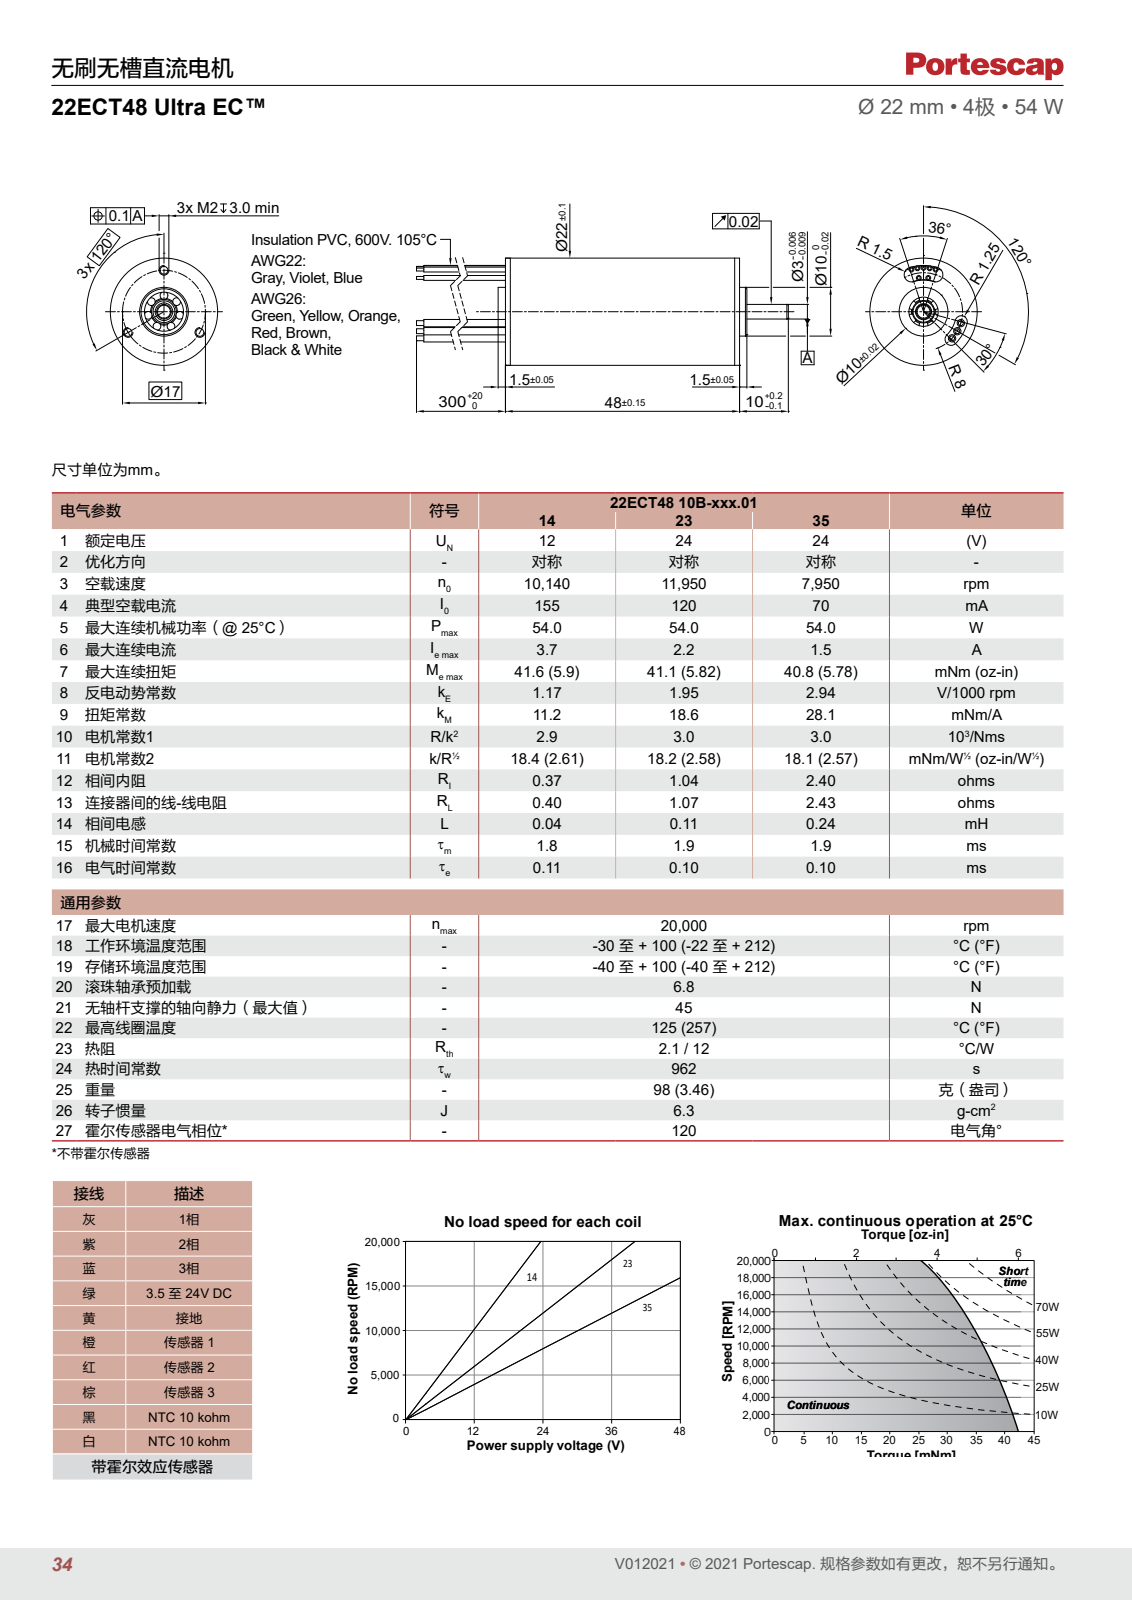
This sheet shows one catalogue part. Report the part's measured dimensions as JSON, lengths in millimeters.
{"part_name": "22ECT_48", "step_written_by": "SolidWorks 2018 (AUTOMOTIVE_DESIGN)", "units": "millimeters", "bodies": {"solids": 15, "faces": 118, "planar": 48, "cylindrical": 49, "other": 21}, "overall_size": [356.5, 22, 22], "volume_mm3": 21533, "surface_area_mm2": 23120, "round_holes": [[1.6, 3], [6, 1], [8, 1], [21, 1]], "round_bosses_or_shafts": [[0.6, 10], [1, 7], [1.5, 3], [22, 1], [10, 1], [3, 1]], "partial_cylinders_radius": [[1.25, 2], [1.5, 2], [6.5, 1], [6.75, 1], [9.25, 1], [9.5, 1]], "face_to_face_distances": [40.65, 2.5, 45.5, 4.85, 43.15, 48, 47, 1.5, 47.3, 44.8], "hole_center_spacings": [8.5, 14.72]}
